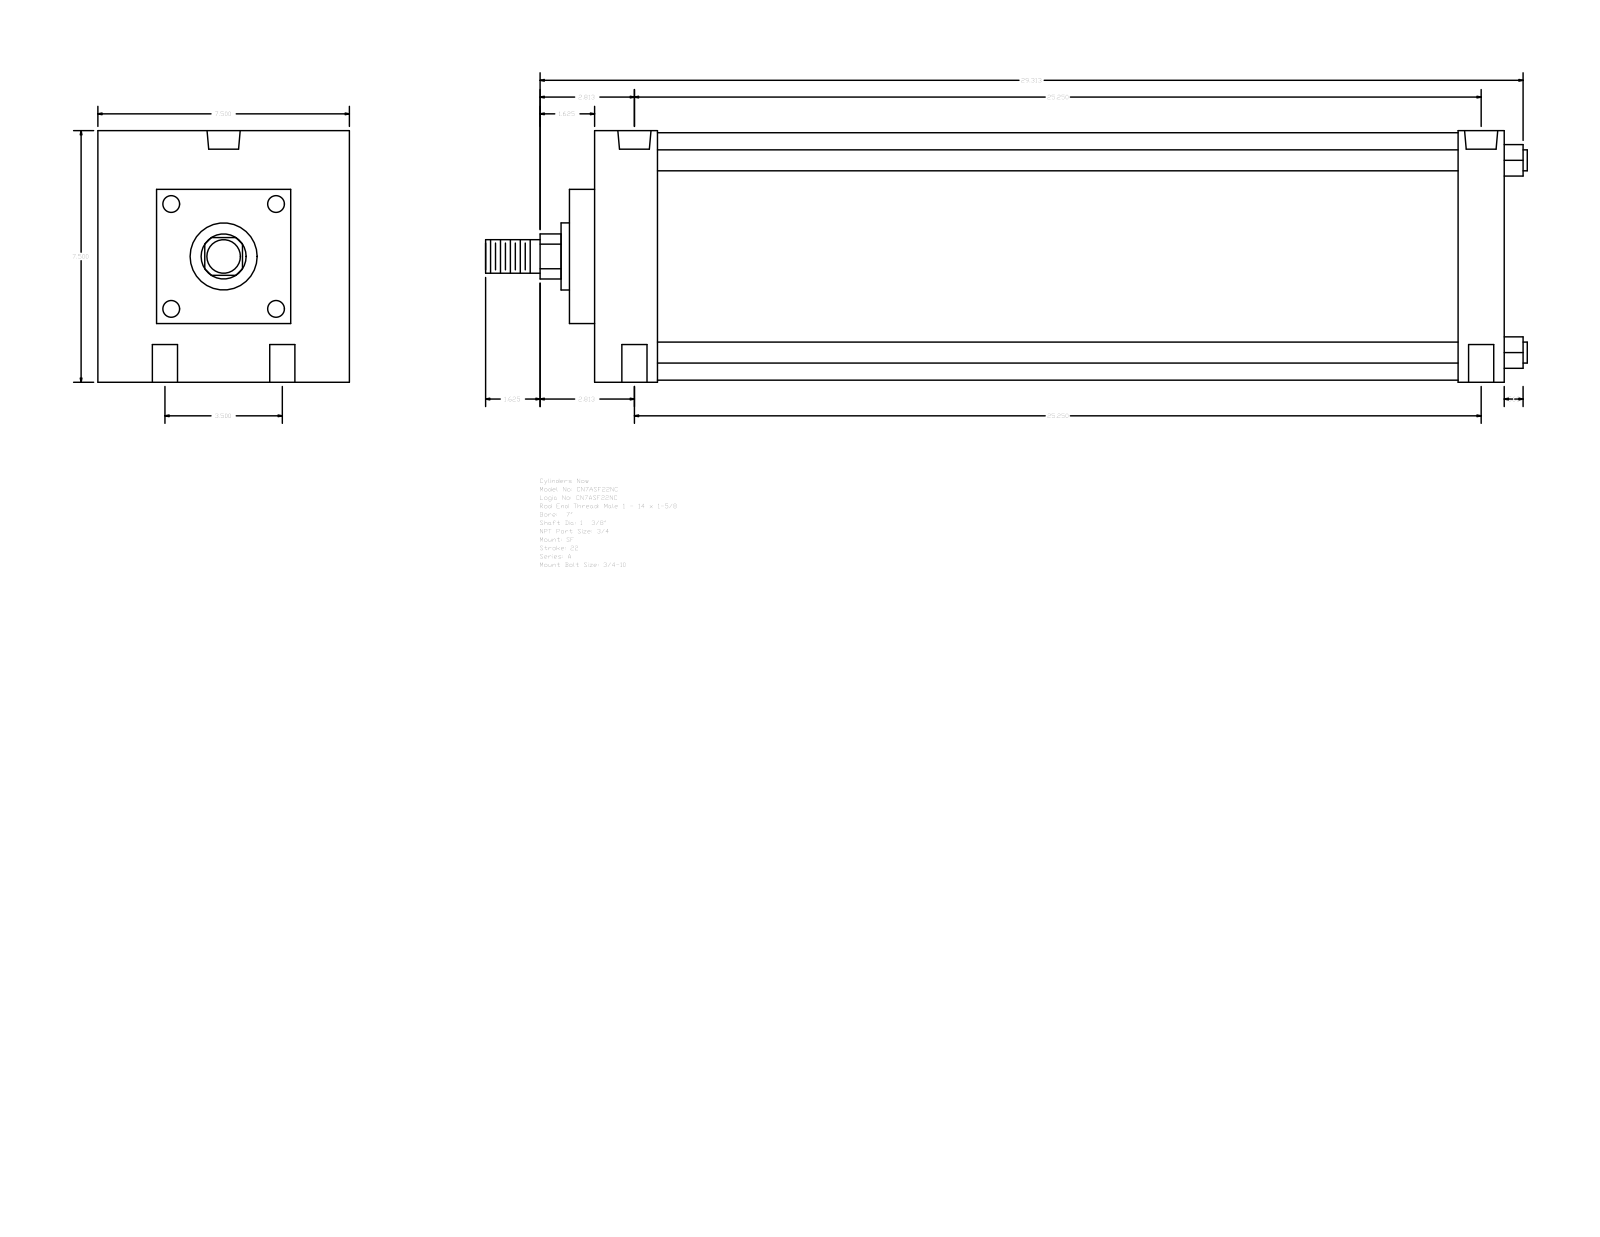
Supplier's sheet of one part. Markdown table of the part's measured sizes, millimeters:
| quantity | value |
| --- | --- |
| part name | A_SF__0700_1.375 |
| STEP written by | GSSL Pune (CONFIG_CONTROL_DESIGN) |
| units | millimeters |
| bodies | 0 solids, 93 faces (67 planar, 26 cylindrical, 0 other) |
| overall size | 788.99 × 190.5 × 190.5 |
| round holes (diameter × count) | 19.05 × 4, 15.08 × 2, 25.12 × 2 |
| round bosses / shafts (diameter × count) | 15.88 × 4, 187.32 × 1, 50.8 × 1, 34.92 × 1, 25.4 × 1 |
| partial cylindrical surfaces (radius × count) | 17.06 × 1 |
| main face-to-face distances | 190.5, 688.98, 19.04, 708.02, 66.67, 673.1, 47.63, 654.06, 606.43, 641.35 |
| hole center spacings | 44.45, 642.89, 641.35, 88.9, 647.48, 630.23 |
